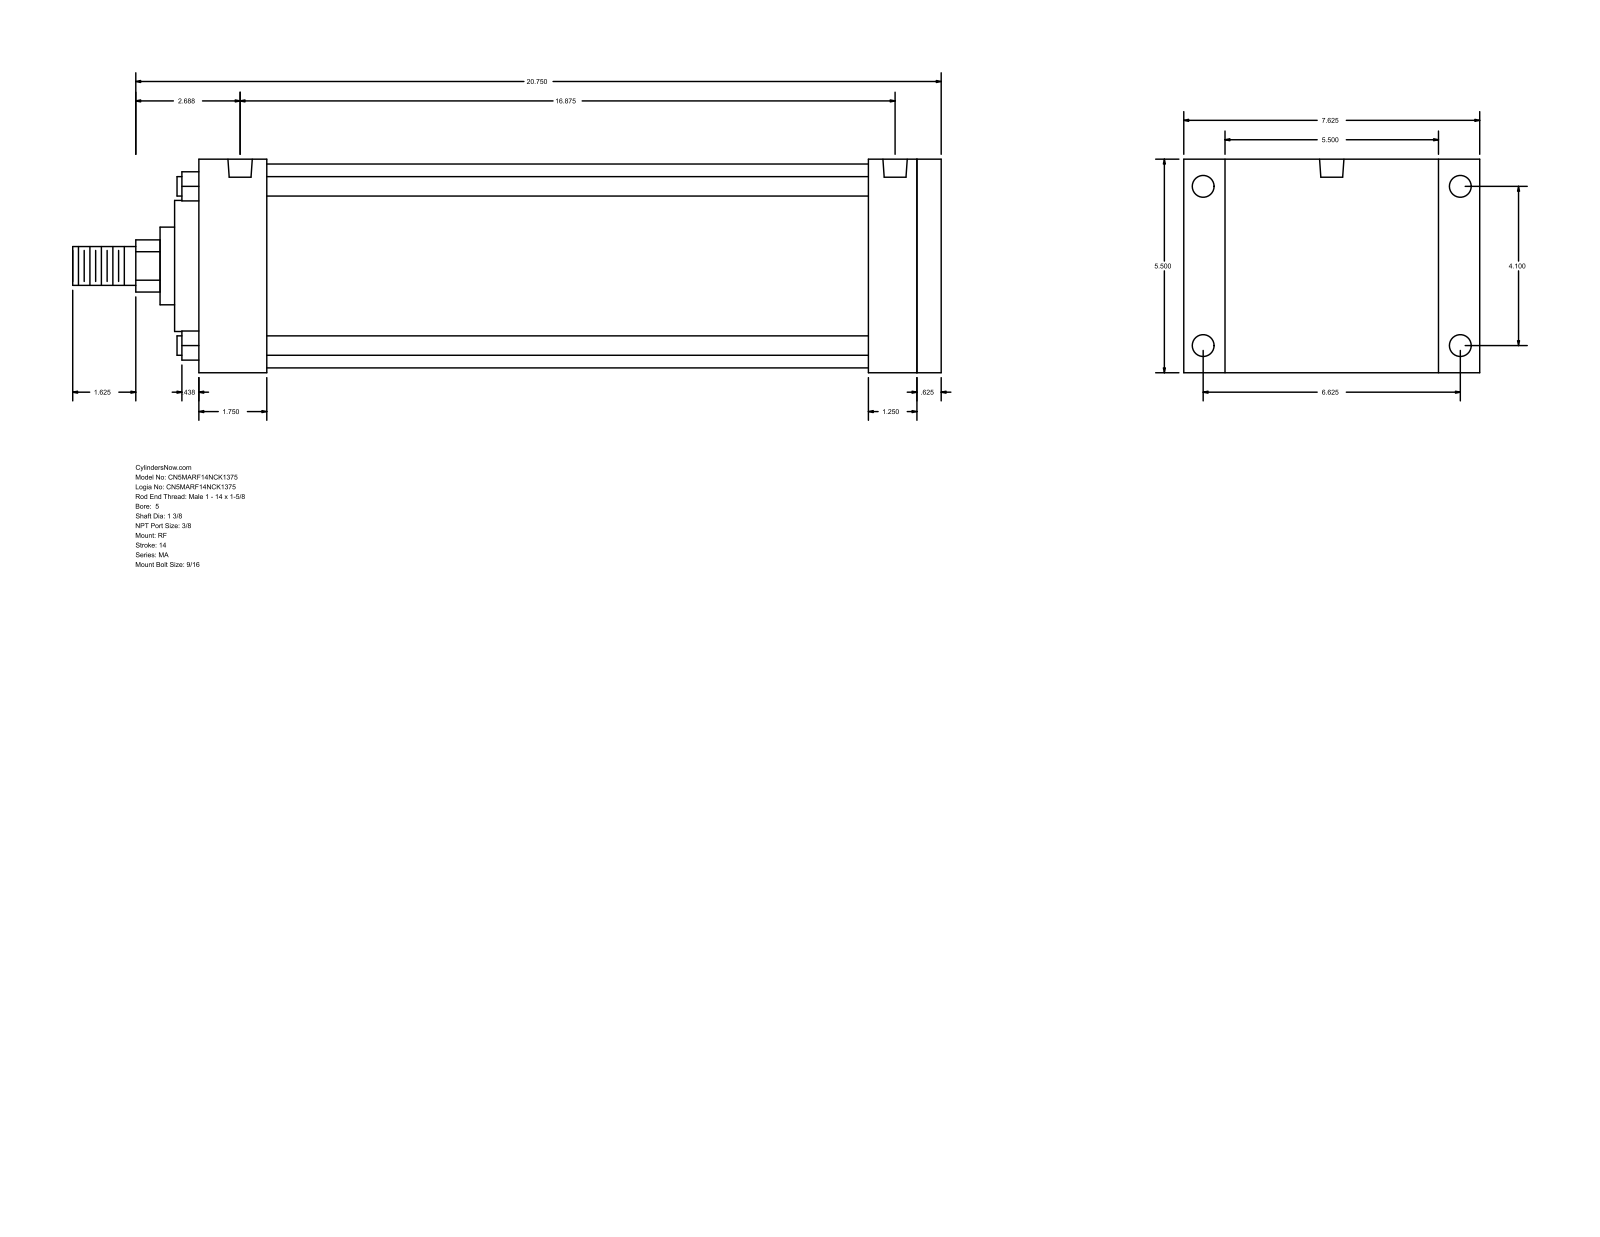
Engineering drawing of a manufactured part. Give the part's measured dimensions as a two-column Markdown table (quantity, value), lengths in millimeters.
| quantity | value |
| --- | --- |
| part name | MA_RF__0500_1.375 |
| STEP written by | GSSL Pune (CONFIG_CONTROL_DESIGN) |
| units | millimeters |
| bodies | 0 solids, 94 faces (65 planar, 29 cylindrical, 0 other) |
| overall size | 568.33 × 193.68 × 139.7 |
| round holes (diameter × count) | 11.11 × 4, 14.29 × 4, 15.93 × 2 |
| round bosses / shafts (diameter × count) | 12.7 × 4, 133.35 × 1, 85.72 × 1, 50.8 × 1, 34.92 × 1, 25.4 × 1 |
| partial cylindrical surfaces (radius × count) | 17.06 × 1 |
| main face-to-face distances | 139.7, 485.78, 15.87, 469.91, 44.45, 425.46, 441.33, 438.16, 393.71, 31.75 |
| hole center spacings | 4.77, 104.14, 168.28, 197.9, 419.09, 423.86, 428.63 |
